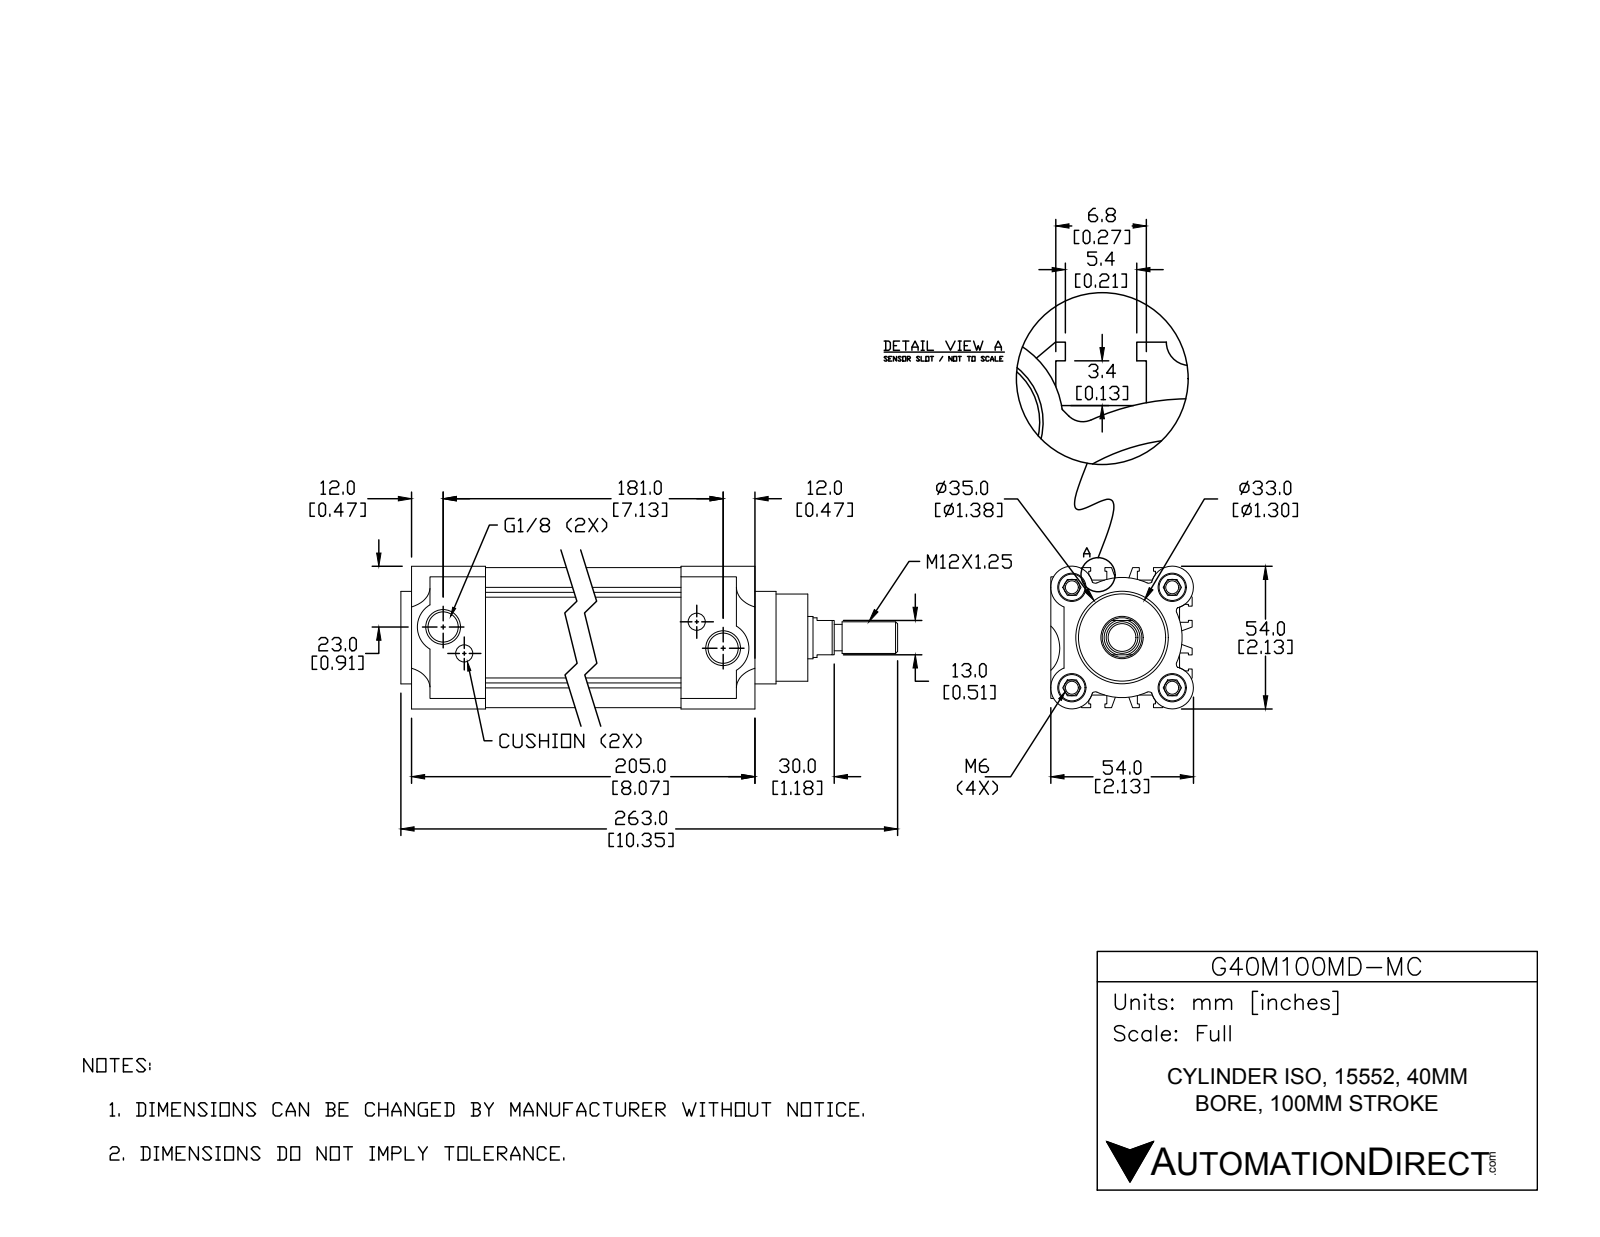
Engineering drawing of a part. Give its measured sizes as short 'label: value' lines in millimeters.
name: 40-HL; G40M100MD-MC; 40121-HR; 40121100-R (+1 more)
written by: SolidWorks 2015 (CONFIG_CONTROL_DESIGN)
unit: mm
bodies: 4 solids, 418 faces (236 planar, 138 cylindrical, 44 other)
size: 263 × 54 × 54
volume: 417 500 mm³; area: 124 300 mm²
holes: 4× ⌀4.9, 4× ⌀10.7, 2× ⌀6.5, 2× ⌀11.5, 1× ⌀16
bosses: 5× ⌀10, 1× ⌀40, 1× ⌀35, 1× ⌀33, 1× ⌀15, 1× ⌀12
rounds: 12× R1.5, 6× R0.1, 4× R7.5, 4× R8, 2× R9.8, 1× R22.5, 1× R22.8
face distances: 48.3, 4.7, 53, 142, 7, 18.4, 24.2, 34.8, 13.9, 35
hole spacings: 26.9, 38, 53.7, 12.8, 14.1, 163.4, 171, 173
